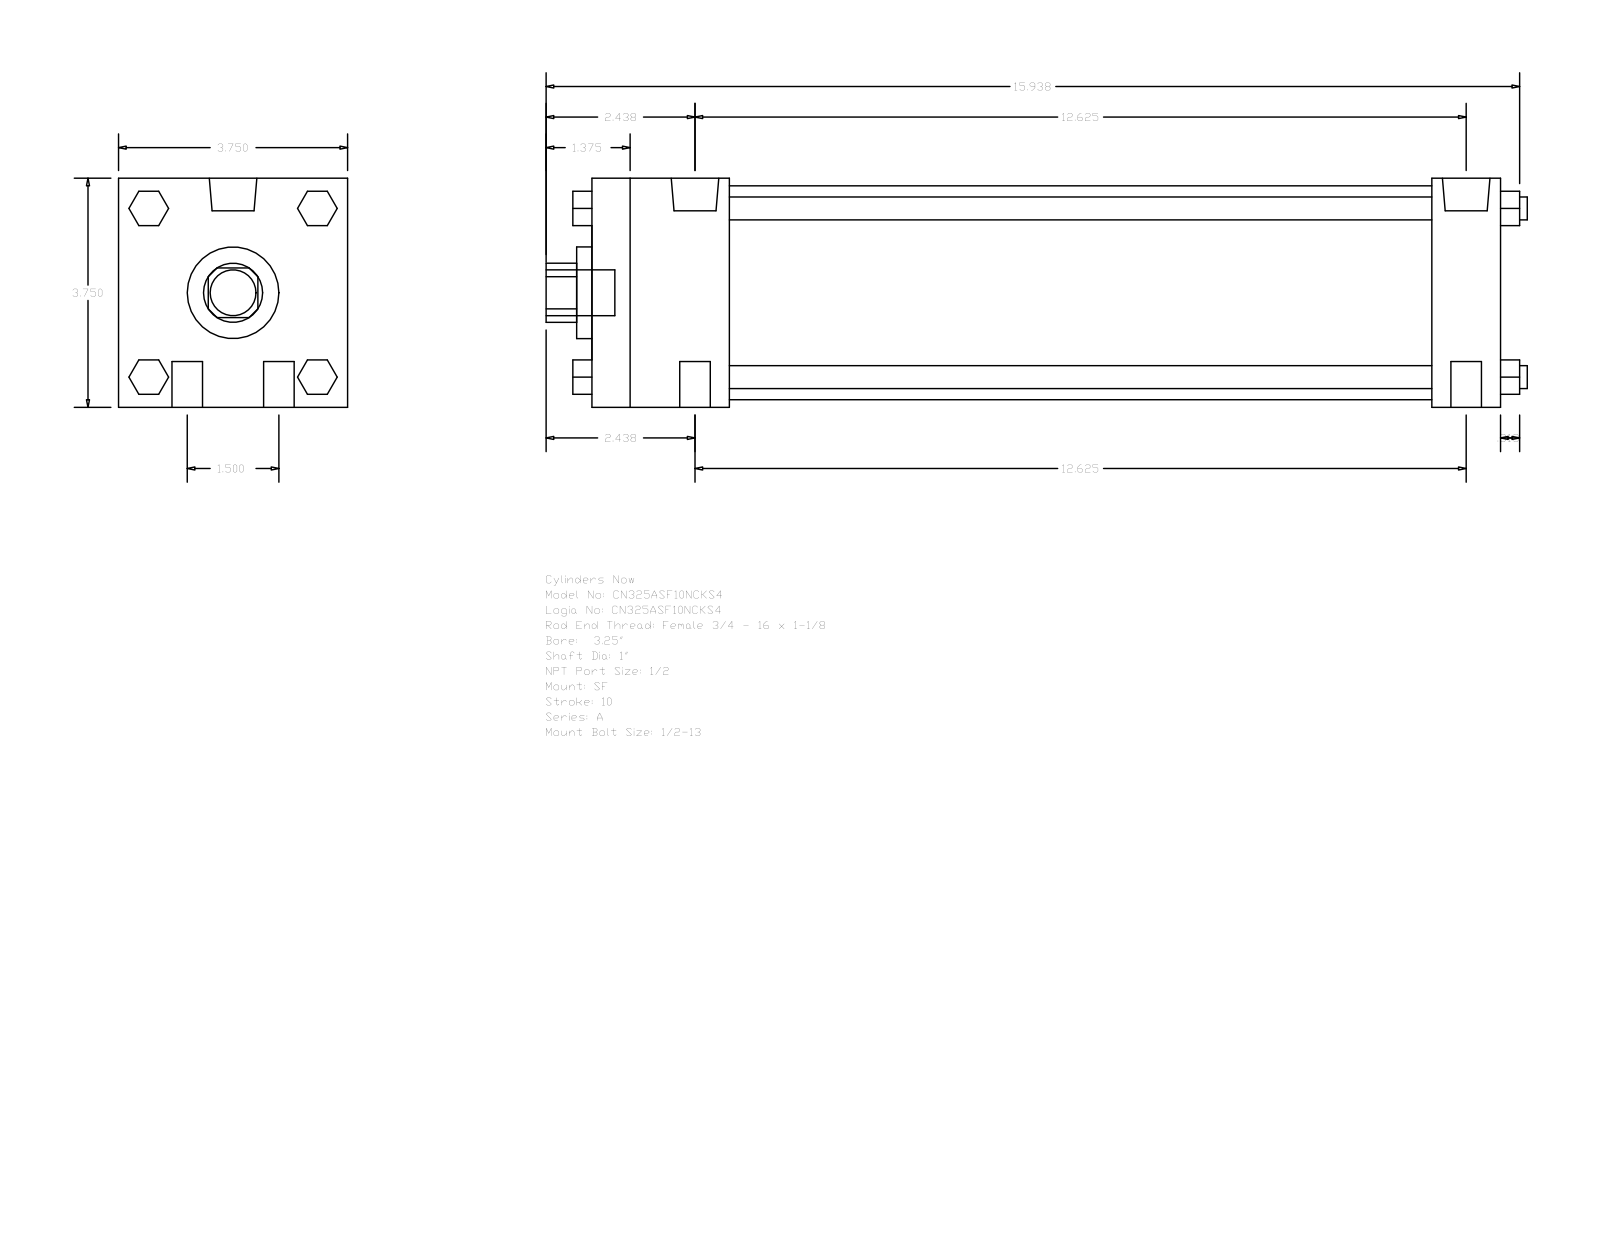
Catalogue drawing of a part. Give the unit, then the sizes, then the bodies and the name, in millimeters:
Units: millimetres
Overall size (bounding box): 407.99 × 95.25 × 95.25
Round holes (diameter × count): ⌀25.4 ×1, ⌀38.1 ×1, ⌀88.9 ×1
Round bosses / shafts (diameter × count): ⌀12.7 ×4, ⌀9.53 ×4, ⌀19.77 ×2, ⌀8.73 ×2, ⌀19.05 ×1
Partial cylindrical surfaces — rounded edges, fillets, slot ends (radius × count): R12.29 ×1
Main face-to-face distances: 95.24, 377.83, 349.25, 28.58, 57.15, 292.1, 320.68, 14.28, 35.05, 60.71
Bodies: 0 solids, 124 faces (94 planar, 30 cylindrical, 0 other)
Part name (STEP PRODUCT): A_SF__0325_1
STEP written by: GSSL Pune (CONFIG_CONTROL_DESIGN)
